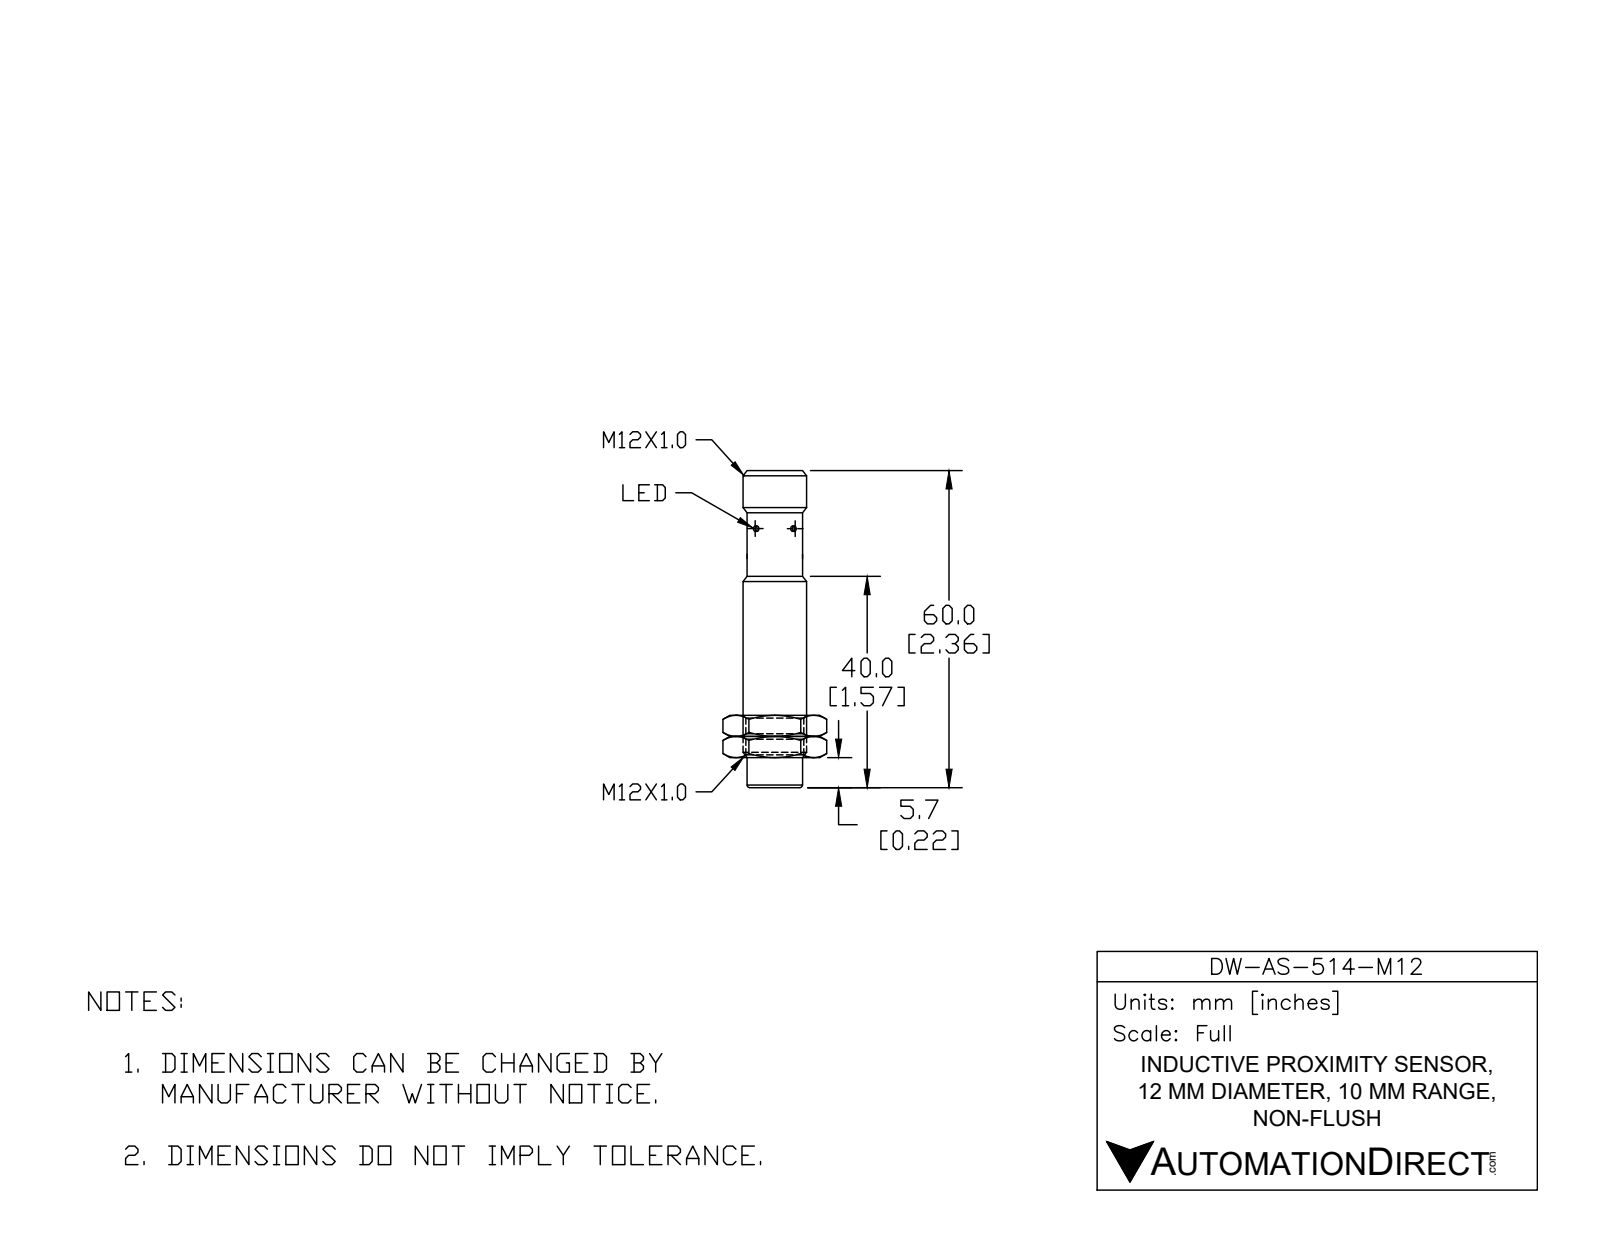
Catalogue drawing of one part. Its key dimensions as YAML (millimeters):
part_name: "DW-AS-514-M12"
step_written_by: "SolidWorks 2017 (AUTOMOTIVE_DESIGN)"
units: millimeters
bodies: {solids: 1, faces: 52, planar: 13, cylindrical: 28, other: 11}
overall_size: [60, 12, 12]
volume: 5750
surface_area: 2895
round_holes:
  - {diameter: 3, count: 2}
  - {diameter: 8.5, count: 1}
round_bosses_or_shafts:
  - {diameter: 1, count: 4}
  - {diameter: 12, count: 1}
  - {diameter: 10.7, count: 1}
  - {diameter: 10.5, count: 1}
partial_cylinders:
  - {radius: 0.5, count: 1}
  - {radius: 0.5, count: 1}
  - {radius: 4.9, count: 1}
  - {radius: 5.2, count: 1}
face_to_face_distances: [51.3, 60, 8.7, 1, 41, 10.3, 19, 52, 11, 0.7]
